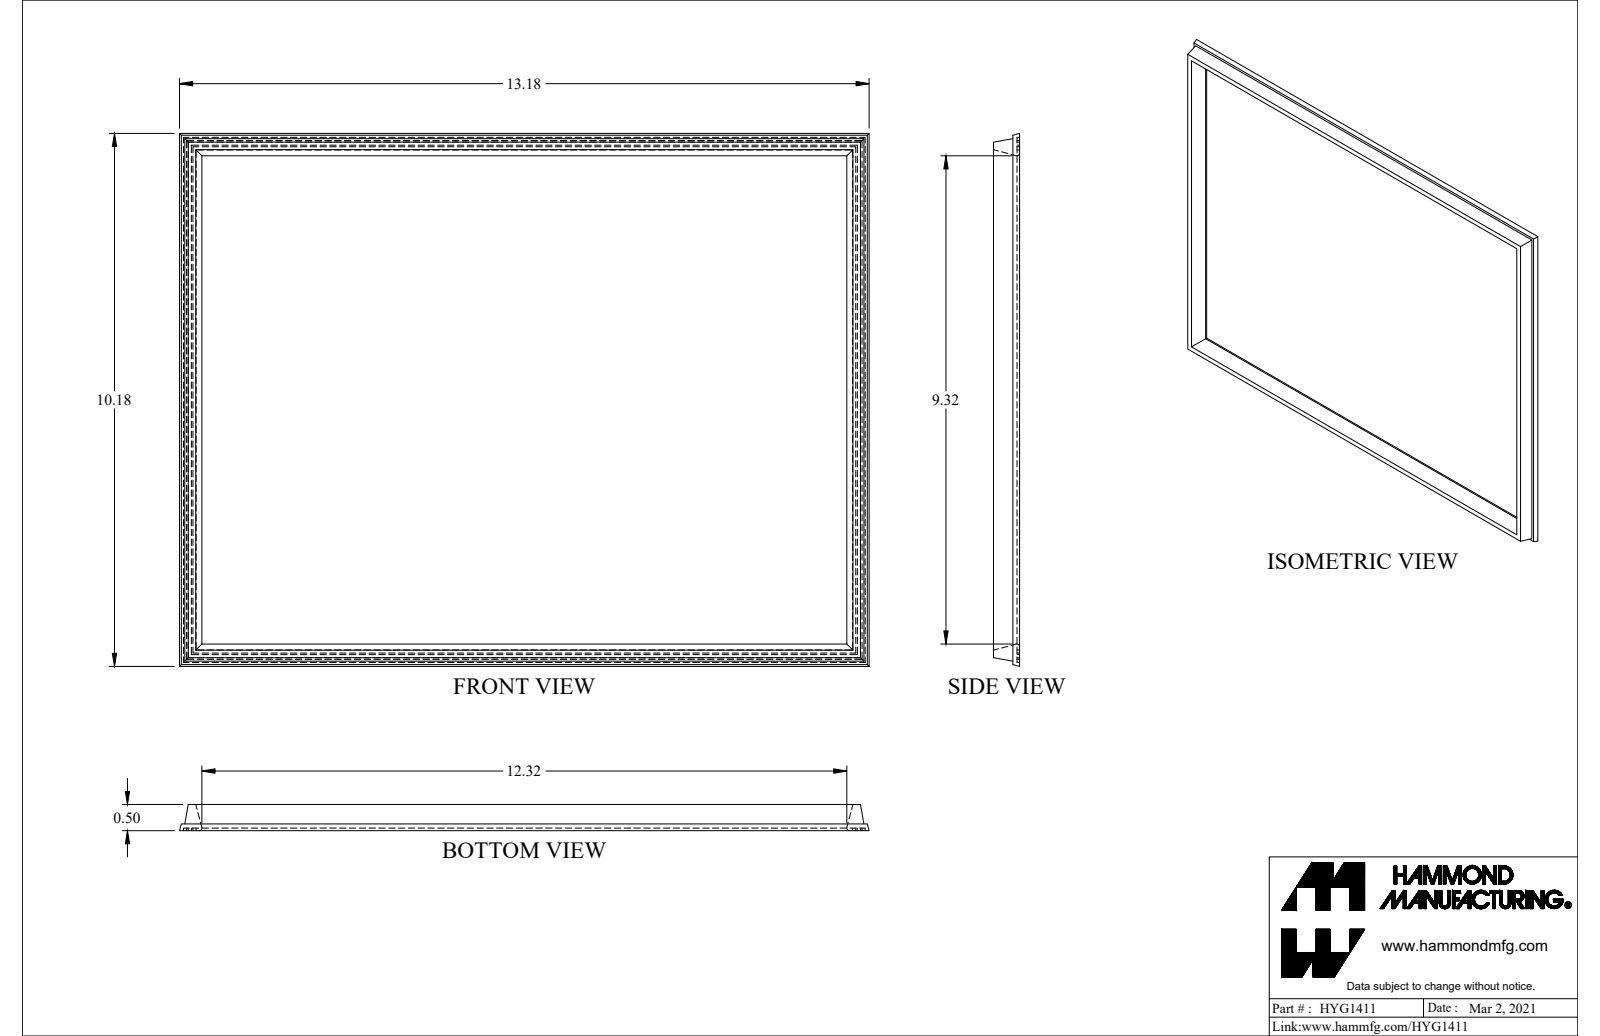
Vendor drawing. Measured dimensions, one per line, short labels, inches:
name: HYG1411
written by: SolidWorks 2021 (AUTOMOTIVE_DESIGN)
unit: in
bodies: 1 solid, 49 faces (45 planar, 4 cylindrical, 0 other)
size: 13.176 × 10.177 × 0.5
volume: 5.67 in³; area: 87.14 in²
rounds: 4× R0.055
face distances: 0.05, 0.5, 0.45, 0.09, 0.06, 0.15, 9.787, 0.03, 9.402, 0.09
